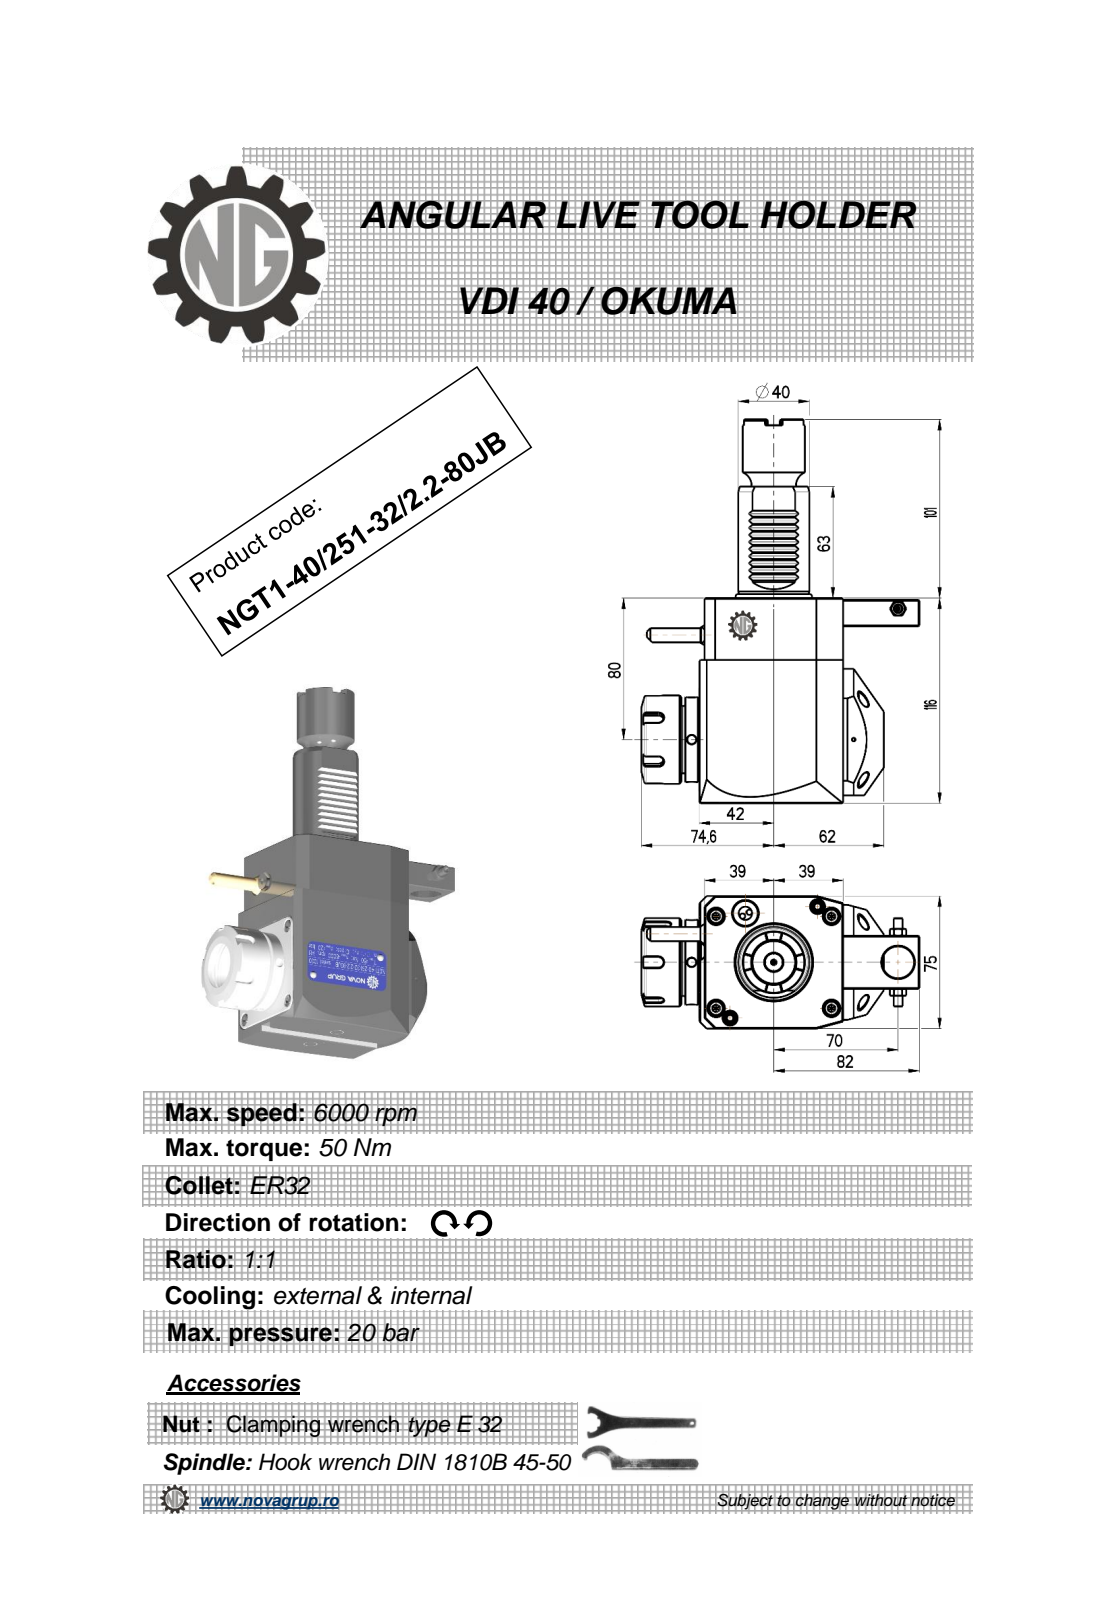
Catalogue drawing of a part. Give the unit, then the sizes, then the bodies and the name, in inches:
Units: inches
Overall size (bounding box): 8.543 × 6.165 × 3.016
Round holes (diameter × count): ⌀0.197 ×3, ⌀0.118 ×1, ⌀0.165 ×1, ⌀0.374 ×1, ⌀0.709 ×1, ⌀0.984 ×1, ⌀1.063 ×1
Round bosses / shafts (diameter × count): ⌀1.969 ×1, ⌀1.89 ×1, ⌀1.614 ×1, ⌀1.575 ×1, ⌀1.378 ×1, ⌀0.394 ×1, ⌀0.353 ×1, ⌀0.315 ×1
Partial cylindrical surfaces — rounded edges, fillets, slot ends (radius × count): R0.01 ×12, R0.012 ×10, R0.008 ×6, R0.118 ×5, R0.02 ×1, R1.575 ×1
Main face-to-face distances: 2.953, 4.567, 3.189, 0.118, 3.071, 4.409, 0.11, 3.181, 0.039, 0.886
Hole centre spacings: 0.824, 1.821, 2.407, 2.756, 2.854, 4.577, 5.425
Volume: 56.56 in³ · Surface area: 119.1 in²
Bodies: 1 solid, 466 faces (209 planar, 92 cylindrical, 165 other)
Part name (STEP PRODUCT): NGT1_40_251_32_2_2_80JB
STEP written by: PRO/ENGINEER BY PARAMETRIC TECHNOLOGY CORPORATION, 2010280 (CONFIG_CONTROL_DESIGN)
